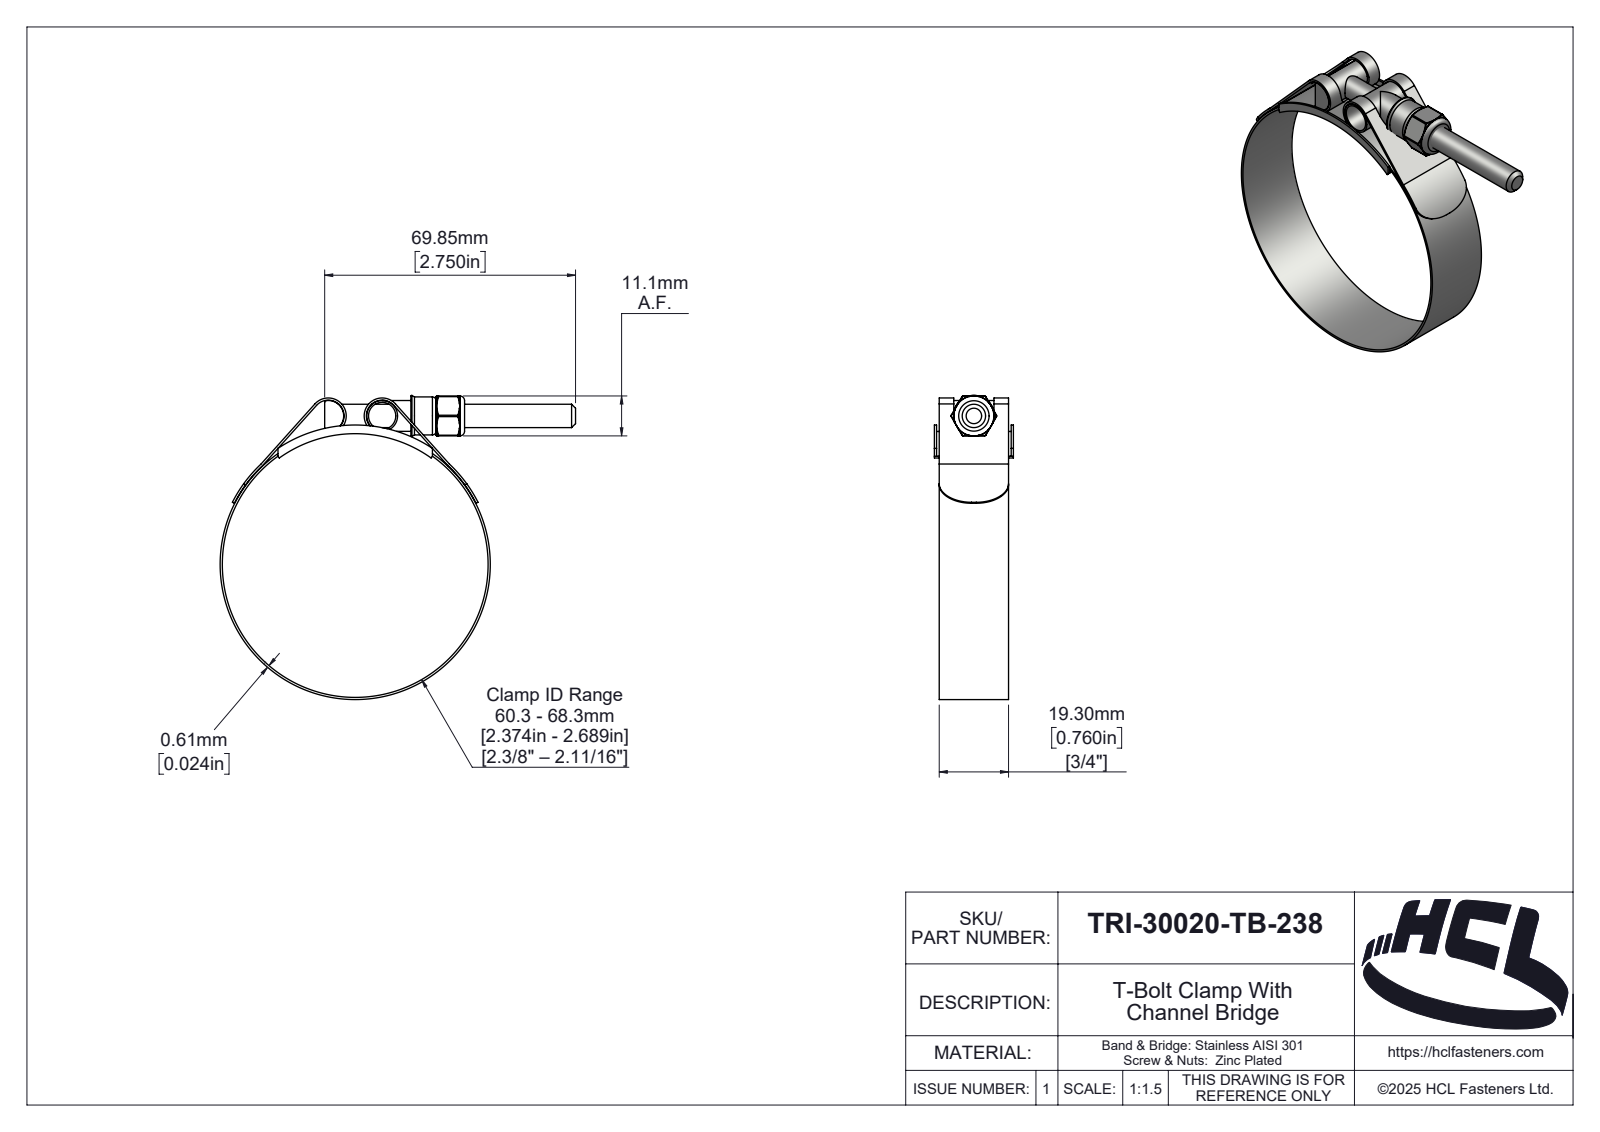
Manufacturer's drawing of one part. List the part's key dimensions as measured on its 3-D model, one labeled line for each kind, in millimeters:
Part name (STEP PRODUCT): TRI-30020-TB-238
STEP written by: SolidWorks 2025 (AUTOMOTIVE_DESIGN)
Units: millimetres
Bodies: 6 solids, 330 faces (44 planar, 122 cylindrical, 164 other)
Overall size (bounding box): 98.96 × 84.66 × 22
Volume: 8 395 mm³ · Surface area: 18 719 mm²
Round holes (diameter × count): ⌀5.4 ×1, ⌀6.35 ×1, ⌀6.5 ×1, ⌀7.58 ×1, ⌀74 ×1
Round bosses / shafts (diameter × count): ⌀8.58 ×2, ⌀75.22 ×1, ⌀10.58 ×1
Partial cylindrical surfaces — rounded edges, fillets, slot ends (radius × count): R0.39 ×6, R0.5 ×2, R4.39 ×2, R5 ×2, R0.59 ×1, R2.42 ×1, R3.03 ×1, R3.19 ×1
Main face-to-face distances: 0.61, 19.3, 0.74, 1.35, 20.65, 21.39, 20.04, 22, 11.11, 20.78
Hole centre spacings: 42
